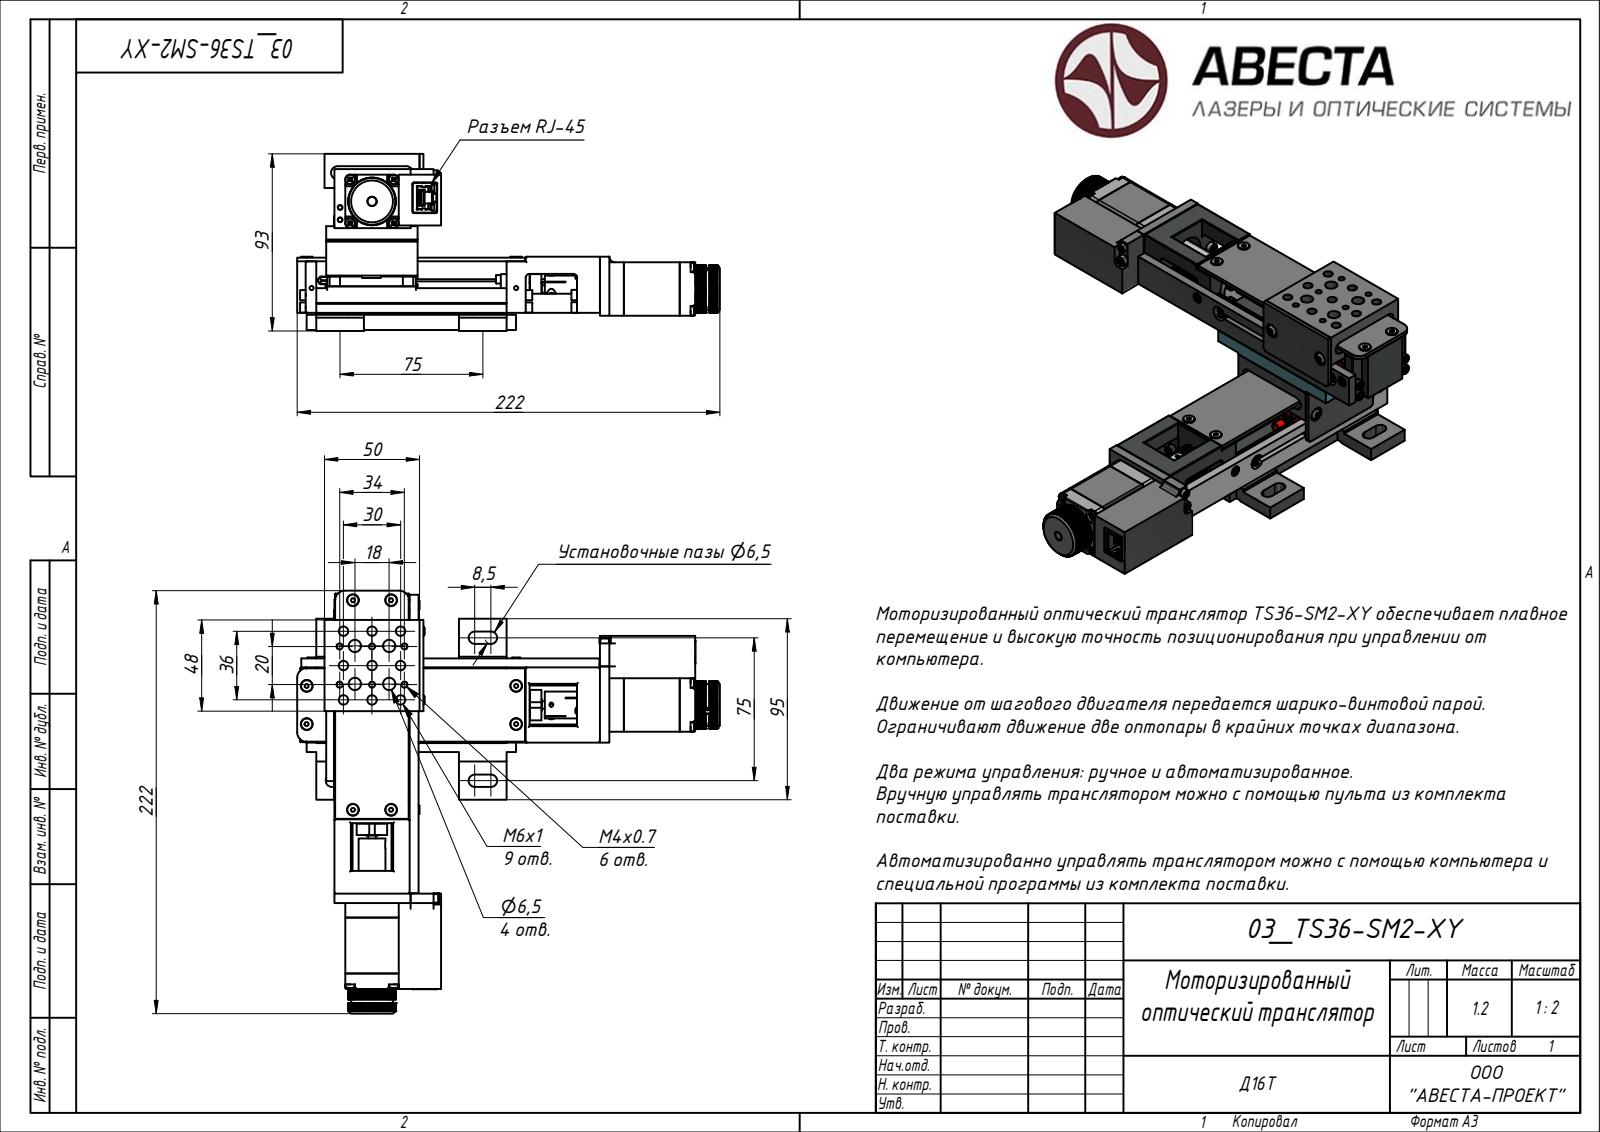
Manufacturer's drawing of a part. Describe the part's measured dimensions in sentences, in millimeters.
Its 3-D file was written by "Rhino 7.34 (AUTOMOTIVE_DESIGN)". It is 1 solid with 4614 faces: 2831 planar, 1248 cylindrical and 535 other. Overall it measures 222 by 222 by 93 millimeters. Its volume is 470 526 cubic millimeters and its surface area 196 126 square millimeters. Round holes: 16 of diameter 3.4, 16 of diameter 6.5, 12 of diameter 3.24, 10 of diameter 1.05, 10 of diameter 2.5, 10 of diameter 4.92, 10 of diameter 7.5, 9 of diameter 2.46, 8 of diameter 3.8, 8 of diameter 5, 6 of diameter 2.15, 6 of diameter 2.46. Round bosses or shafts: 20 of diameter 4.5, 12 of diameter 3, 10 of diameter 6, 10 of diameter 5.5, 8 of diameter 5.3, 6 of diameter 5, 6 of diameter 2.5, 4 of diameter 5.7. Partial cylindrical surfaces (rounded edges, fillets, slot ends): 72 of radius 0.5, 20 of radius 2.5, 20 of radius 3, 16 of radius 2, 8 of radius 1, 8 of radius 3.25, 4 of radius 1.75, 4 of radius 2.4. The main face-to-face distances are 46, 0.5, 2, 2.5, 38, 26.5, 48, 46.5, 19.5, 27. The hole center spacings are 1, 20, 18, 2, 9, 13.04, 17, 18.03.
